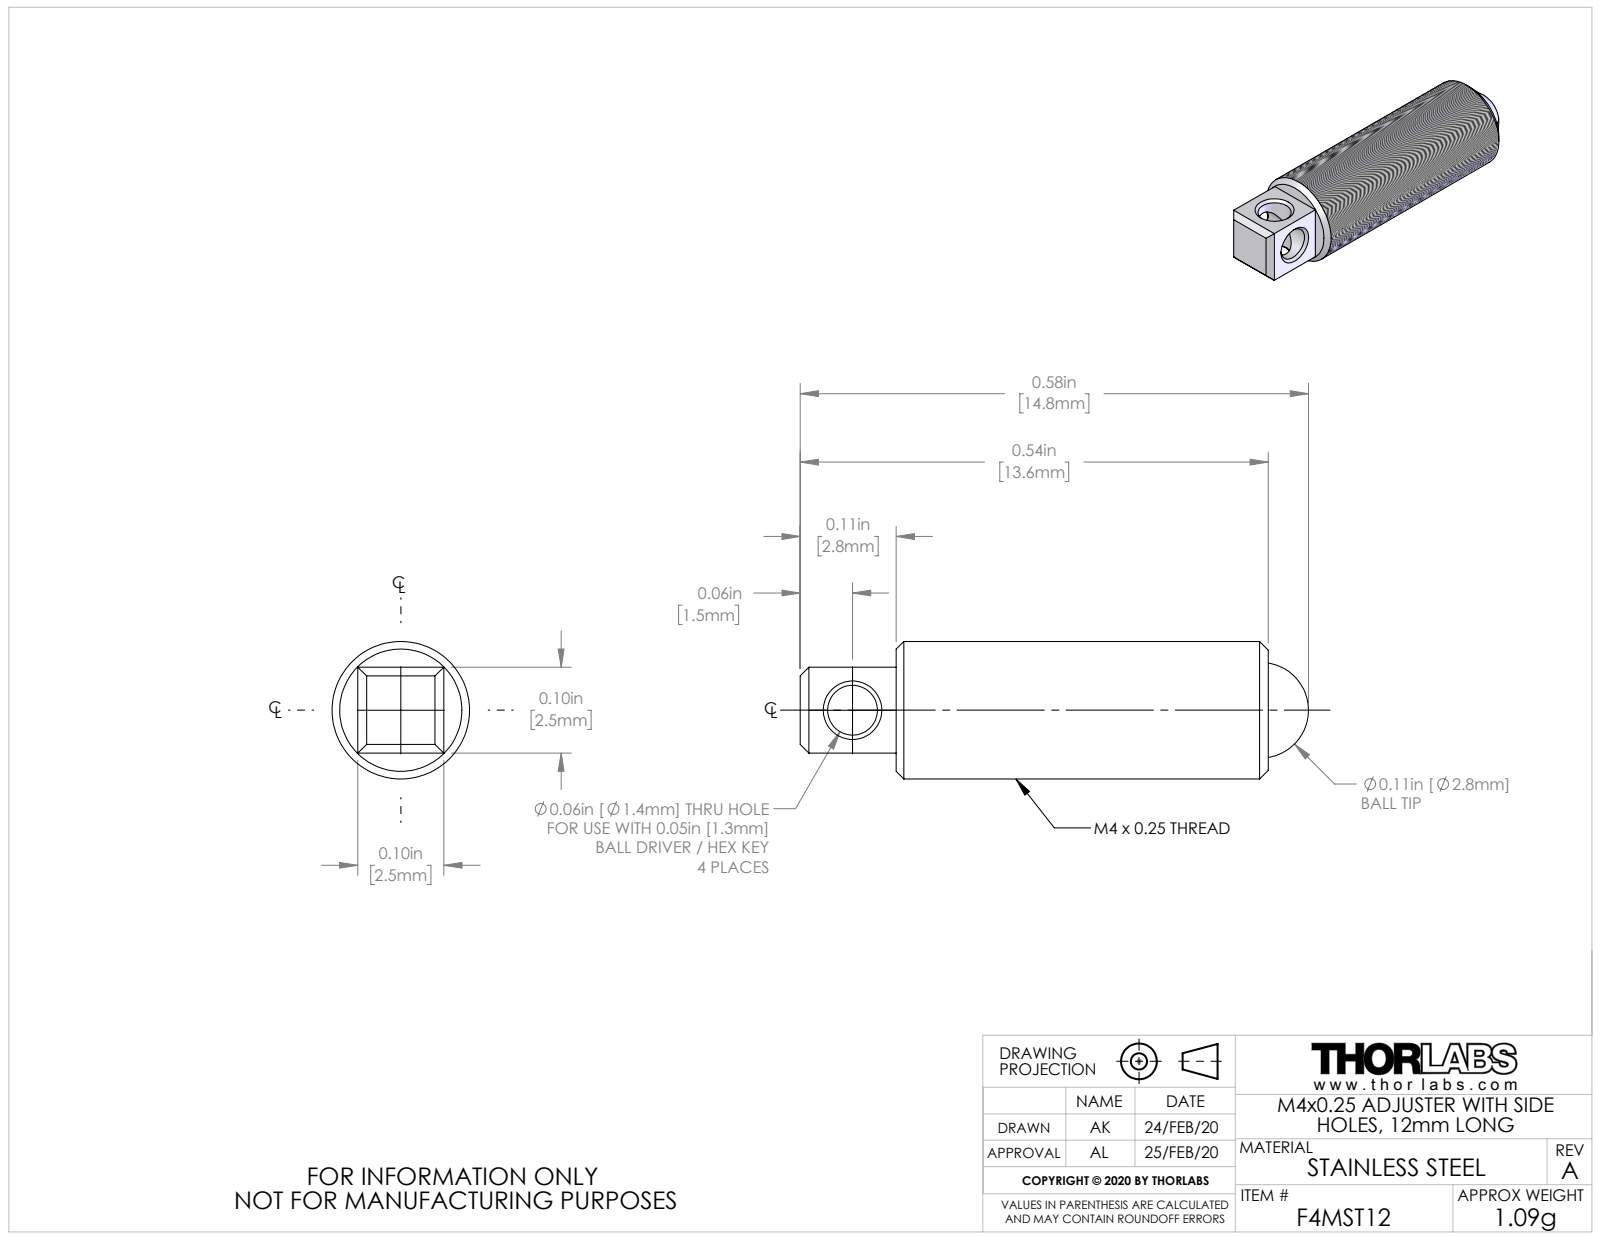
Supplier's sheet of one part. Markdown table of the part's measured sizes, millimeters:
| quantity | value |
| --- | --- |
| part name | TTN203598-E0W |
| STEP written by | SolidWorks 2018 (AUTOMOTIVE_DESIGN) |
| units | millimeters |
| bodies | 2 solids, 41 faces (11 planar, 12 cylindrical, 18 other) |
| overall size | 14.8 × 4 × 4 |
| volume | 100 mm³ |
| surface area | 224 mm² |
| round holes (diameter × count) | 1.4 × 2, 2.8 × 1 |
| round bosses / shafts (diameter × count) | 4 × 1 |
| main face-to-face distances | 2.5, 2.8, 10.8, 13.6 |
